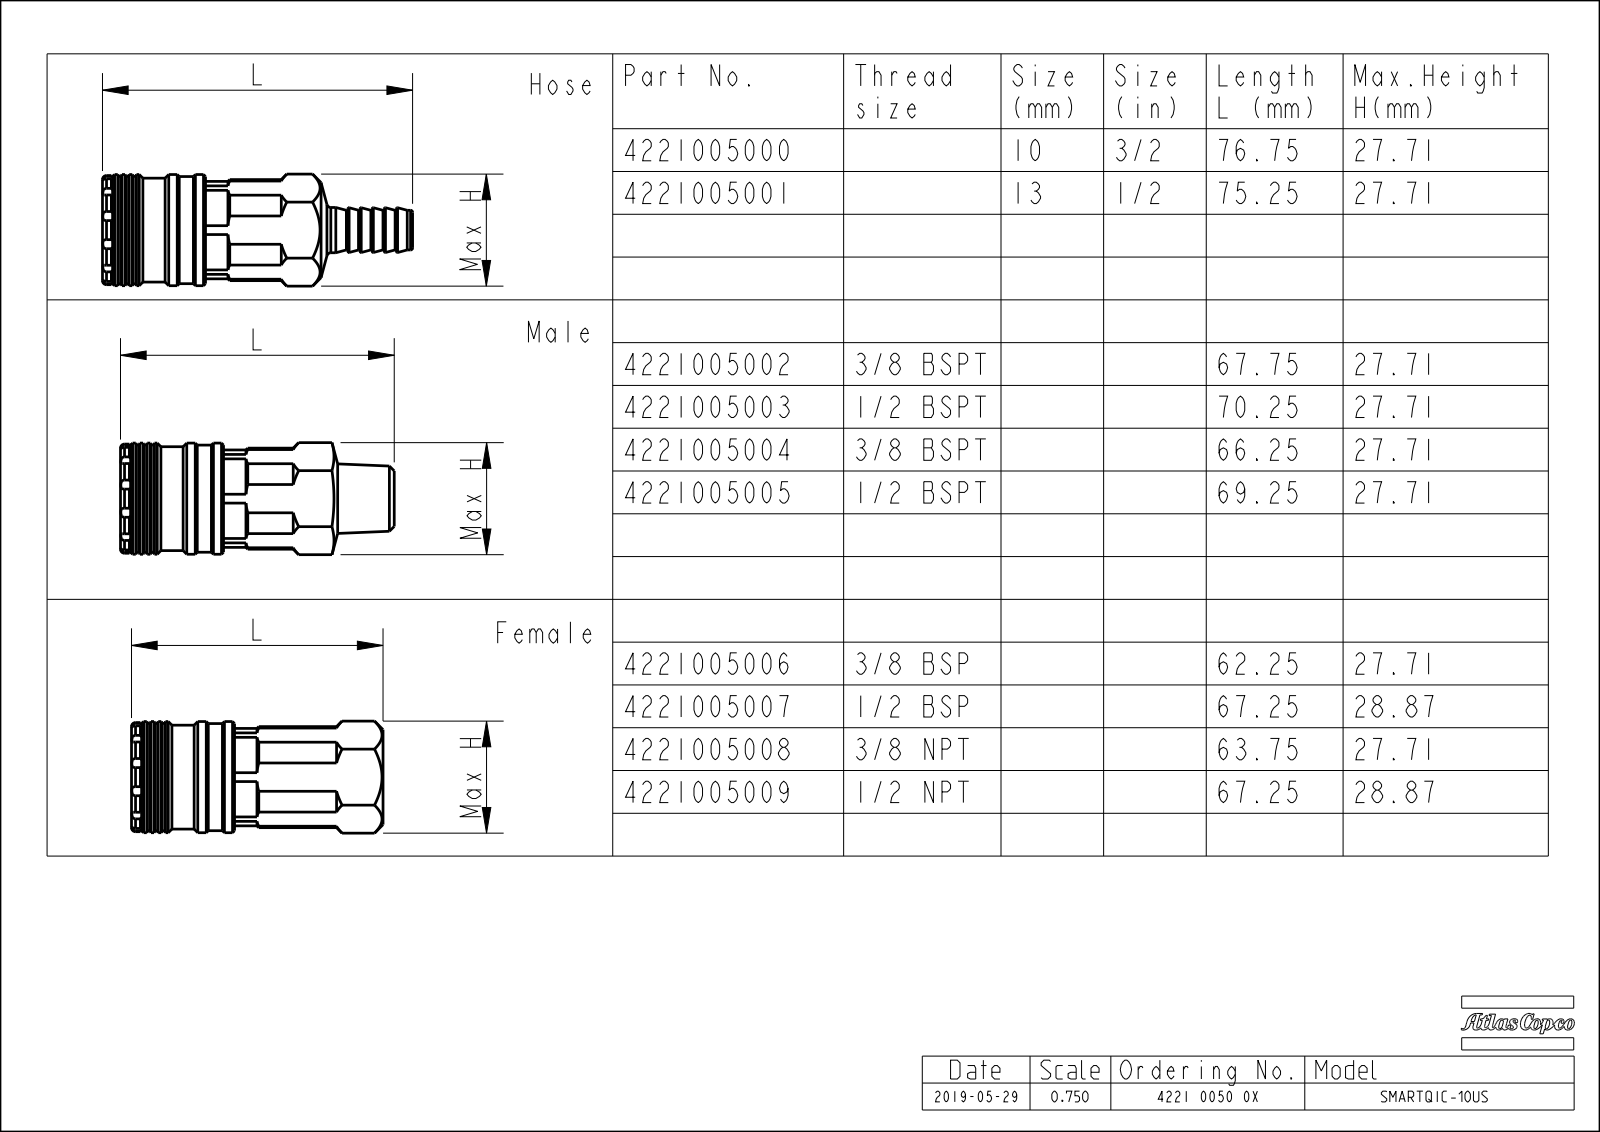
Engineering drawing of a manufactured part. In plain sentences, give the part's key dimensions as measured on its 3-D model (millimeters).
The part is named "4221005009". Its 3-D file was written by "CREO PARAMETRIC BY PTC INC, 2018100 (AP242_MANAGED_MODEL_BASED_3D_ENGINEERING_MIM_LF)". It is 1 solid with 137 faces: 11 planar, 50 cylindrical and 76 other. Overall it measures 67.25 by 28.87 by 27.5 millimeters. Its volume is 35 272 cubic millimeters and its surface area 7 103 square millimeters. Round holes: 1 of diameter 15.22. Round bosses or shafts: 1 of diameter 27.5, 1 of diameter 26.5, 1 of diameter 25.7, 1 of diameter 24.1. Partial cylindrical surfaces (rounded edges, fillets, slot ends): 12 of radius 1.5, 1 of radius 13, 1 of radius 13.5. The main face-to-face distances are 25, 67.25, 2.5, 64.75, 25.5, 23, 41.75.
